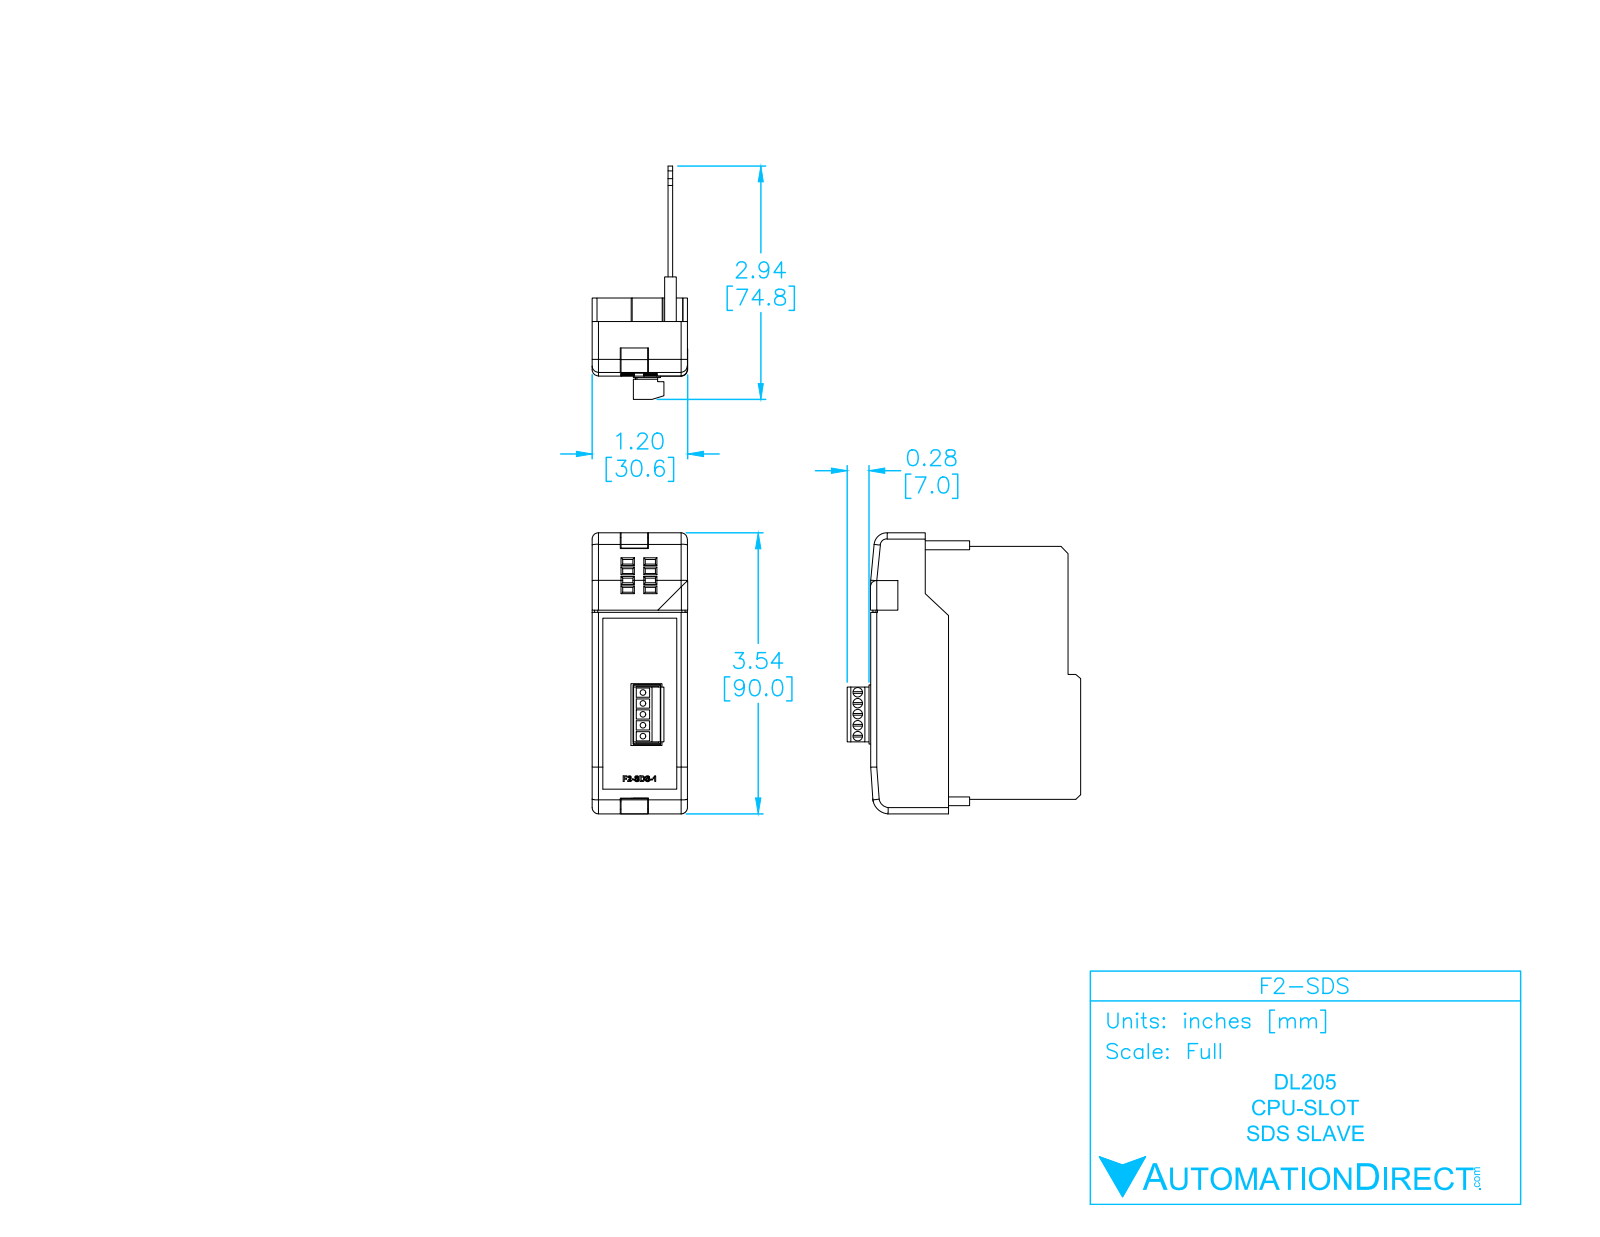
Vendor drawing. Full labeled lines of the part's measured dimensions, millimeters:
Part name (STEP PRODUCT): F2-SDS-1
STEP written by: SolidWorks 2009 (AUTOMOTIVE_DESIGN)
Units: millimetres
Bodies: 7 solids, 535 faces (346 planar, 129 cylindrical, 60 other)
Overall size (bounding box): 90 × 74.77 × 30.55
Volume: 19 276 mm³ · Surface area: 28 993 mm²
Round holes (diameter × count): ⌀1.72 ×5, ⌀3 ×5
Partial cylindrical surfaces — rounded edges, fillets, slot ends (radius × count): R0.5 ×28, R2 ×11, R3.15 ×5, R3.4 ×5, R0.25 ×4, R1 ×2, R2.62 ×1, R3.79 ×1
Main face-to-face distances: 1.5, 4.72, 3.22, 6.22, 0.5, 24.28, 29, 30.5, 25.78, 22.78
Hole centre spacings: 3.5, 7, 10.5, 14
